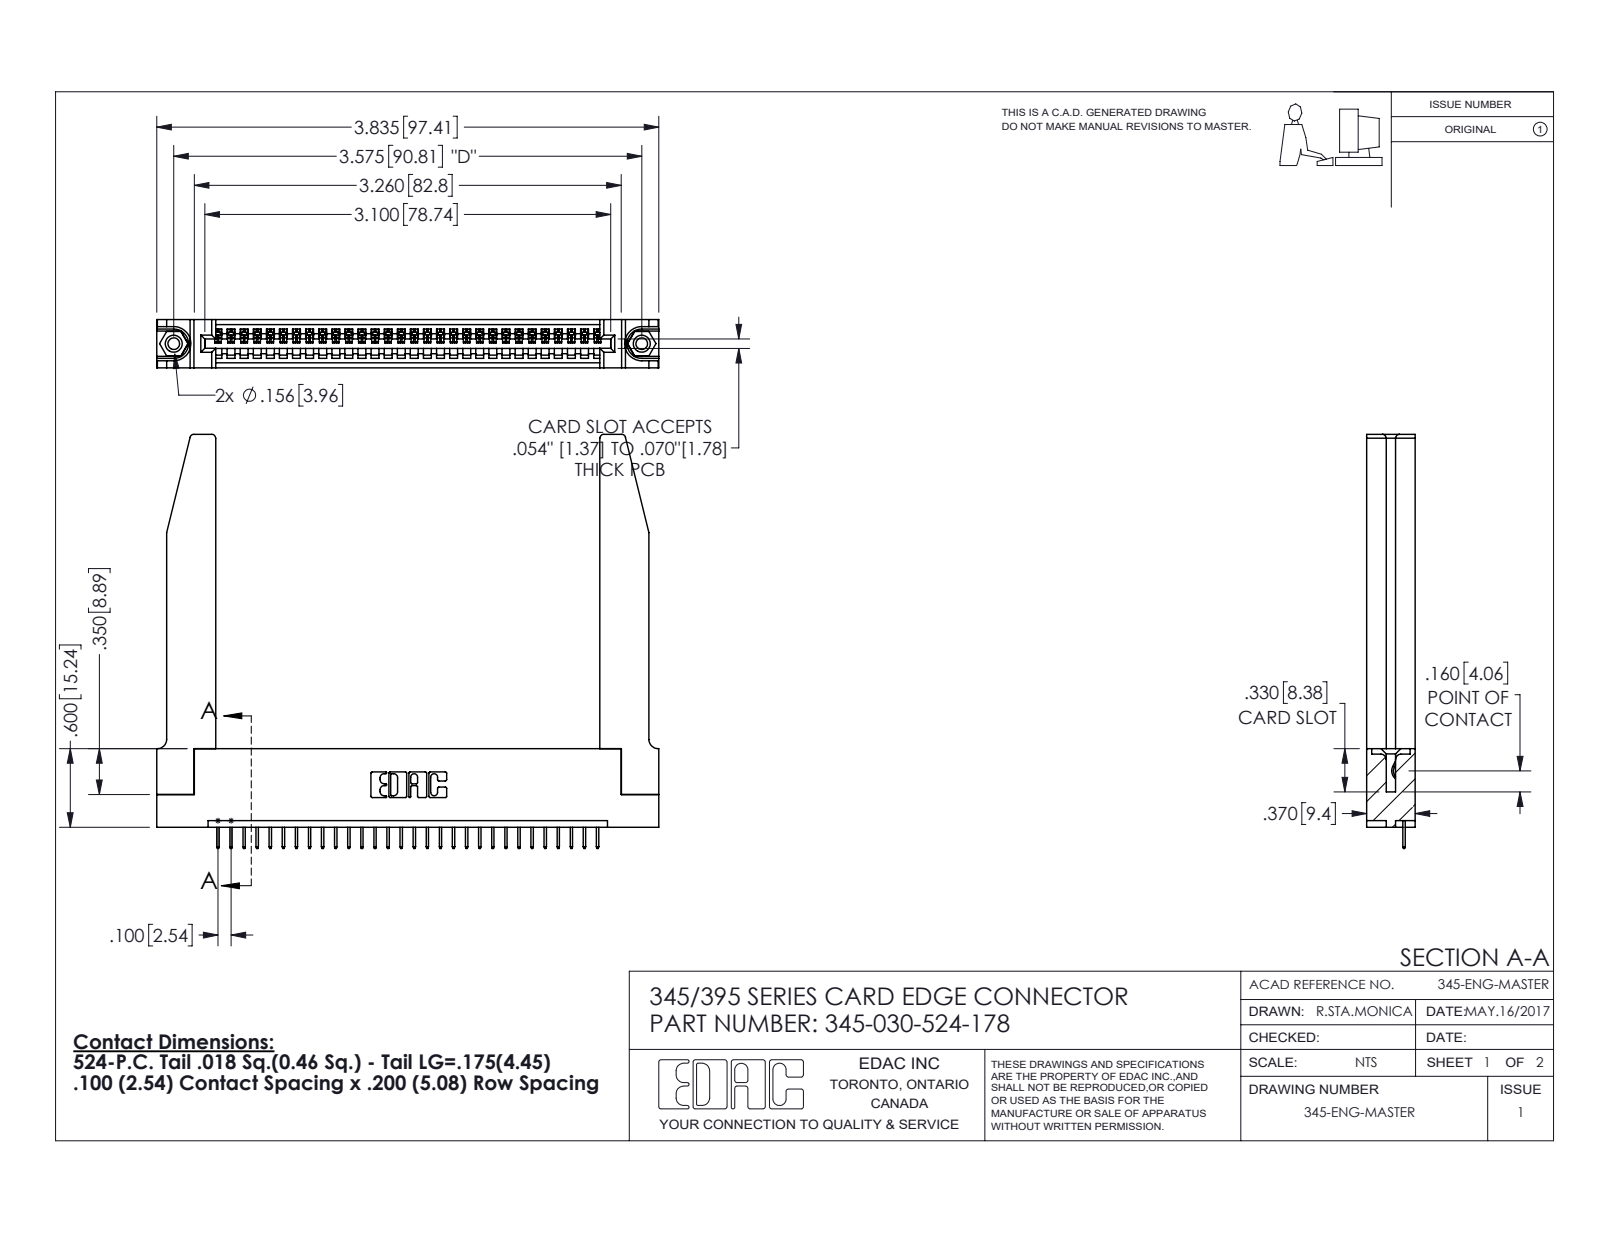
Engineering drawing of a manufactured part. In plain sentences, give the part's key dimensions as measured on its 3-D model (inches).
The part is named "345-250-001_345-250-001-102; 345 Part_Flush Mounting Lugs - 0.156 Dia-TH; 345-292-001_345-293-124; 345-030-524-178 (+1 more)". Its 3-D file was written by "SolidWorks 2016 (CONFIG_CONTROL_DESIGN)". It is 35 solids with 2220 faces: 1602 planar, 566 cylindrical and 52 other. Overall it measures 3.836 by 3.162 by 0.37 inches. Its volume is 1.026 cubic inches and its surface area 28.39 square inches. Round holes: 2 of diameter 0.089, 2 of diameter 0.125, 2 of diameter 0.156, 1 of diameter 0.064. Round bosses or shafts: 2 of diameter 0.155. Partial cylindrical surfaces (rounded edges, fillets, slot ends): 60 of radius 0.006, 22 of radius 0.01, 8 of radius 0.03, 6 of radius 0.007, 6 of radius 0.031, 3 of radius 0.026, 2 of radius 0.031, 2 of radius 0.04. The main face-to-face distances are 0.37, 0.072, 0.298, 0.2, 0.098, 0.272, 0.025, 0.148, 0.15, 0.225. The hole center spacings are 0.27, 3.34, 3.575.
